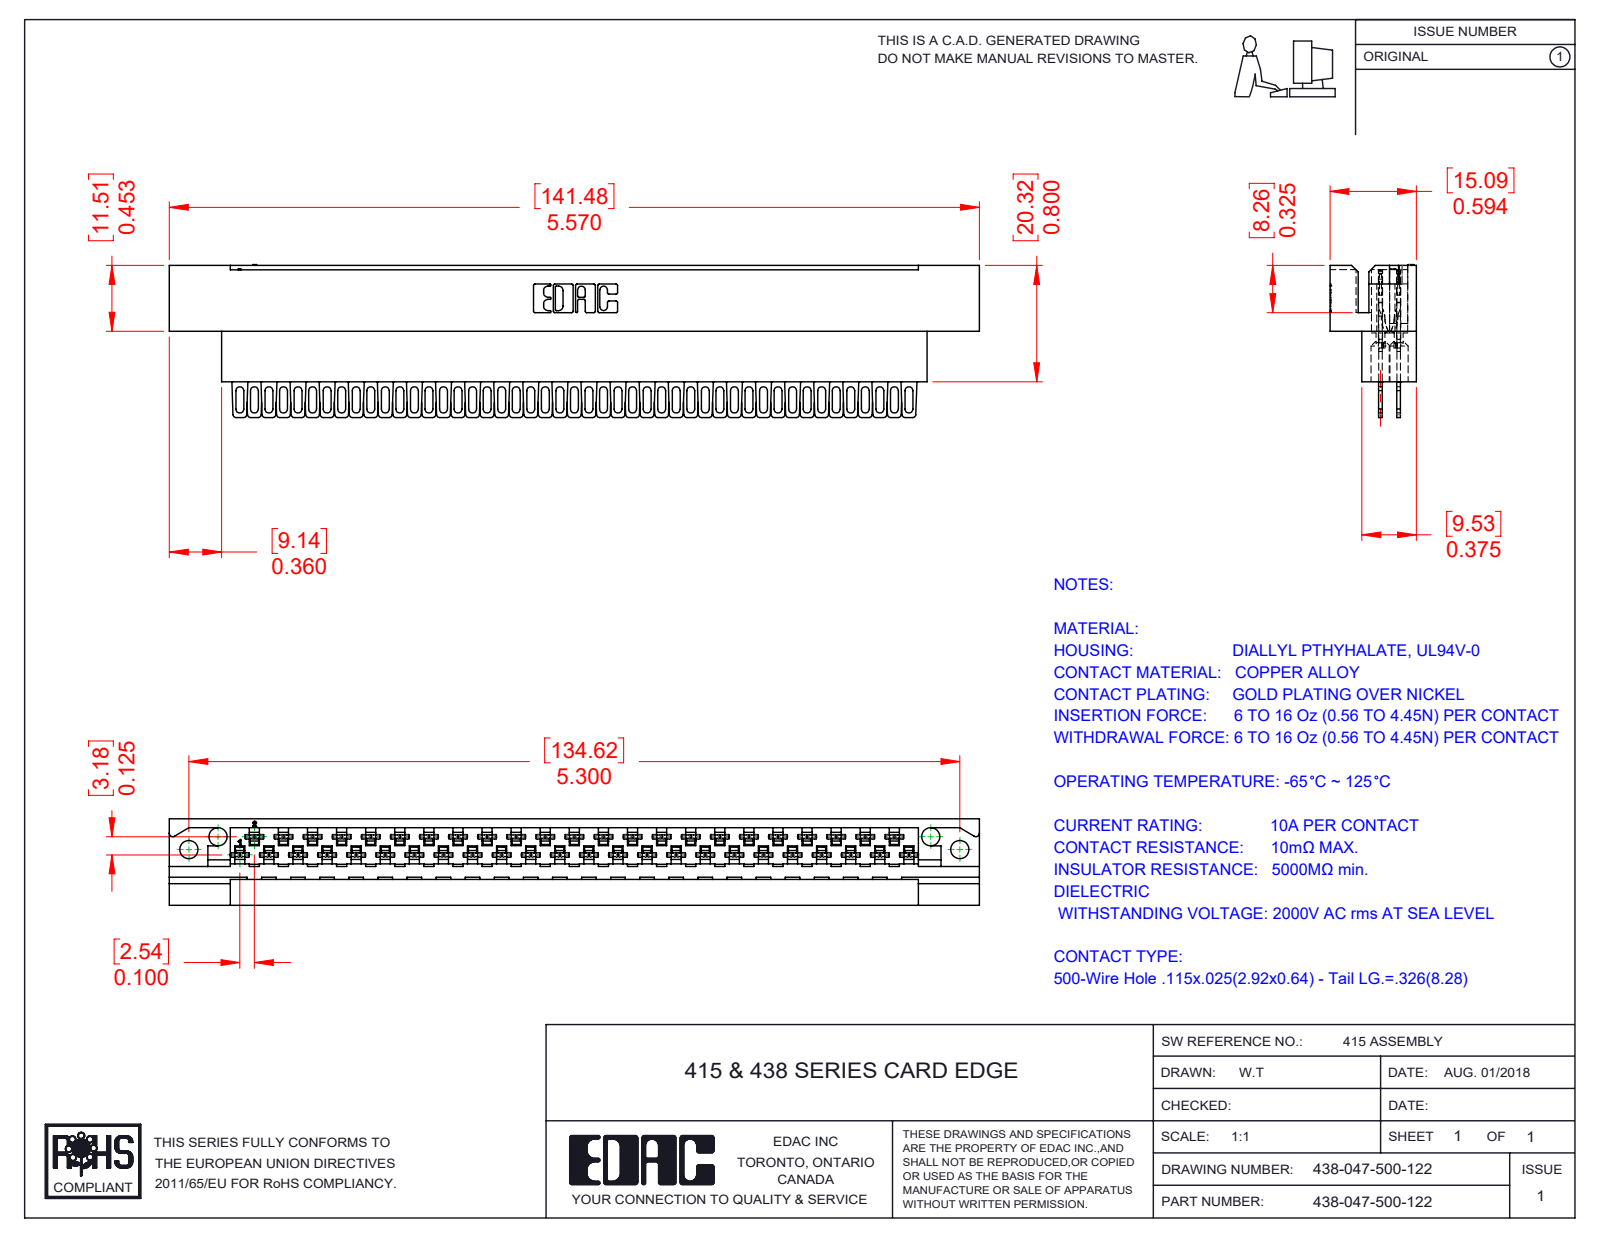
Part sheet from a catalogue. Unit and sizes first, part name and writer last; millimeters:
Units: millimetres
Overall size (bounding box): 141.48 × 26.68 × 15.09
Round holes (diameter × count): ⌀1.27 ×47, ⌀3.3 ×47, ⌀3.17 ×2, ⌀3.18 ×2
Partial cylindrical surfaces — rounded edges, fillets, slot ends (radius × count): R0.3 ×188, R0.56 ×188, R0.18 ×94, R0.2 ×94, R0.41 ×94, R0.51 ×94, R0.69 ×94, R2.03 ×94
Main face-to-face distances: 3.18, 0.61, 1.88, 1.27, 15.09, 1.94, 0.67, 1.21, 6.61, 8.48
Hole centre spacings: 5.08, 10.16, 15.24, 20.32, 25.4, 30.48, 35.56, 2.54
Volume: 25 913 mm³ · Surface area: 31 005 mm²
Bodies: 48 solids, 4954 faces (3094 planar, 1415 cylindrical, 445 other)
Part name (STEP PRODUCT): 438-047-500-122; 516-290-001_500; 438-210-001_438-210-047-112
STEP written by: SolidWorks 2016 (CONFIG_CONTROL_DESIGN)
